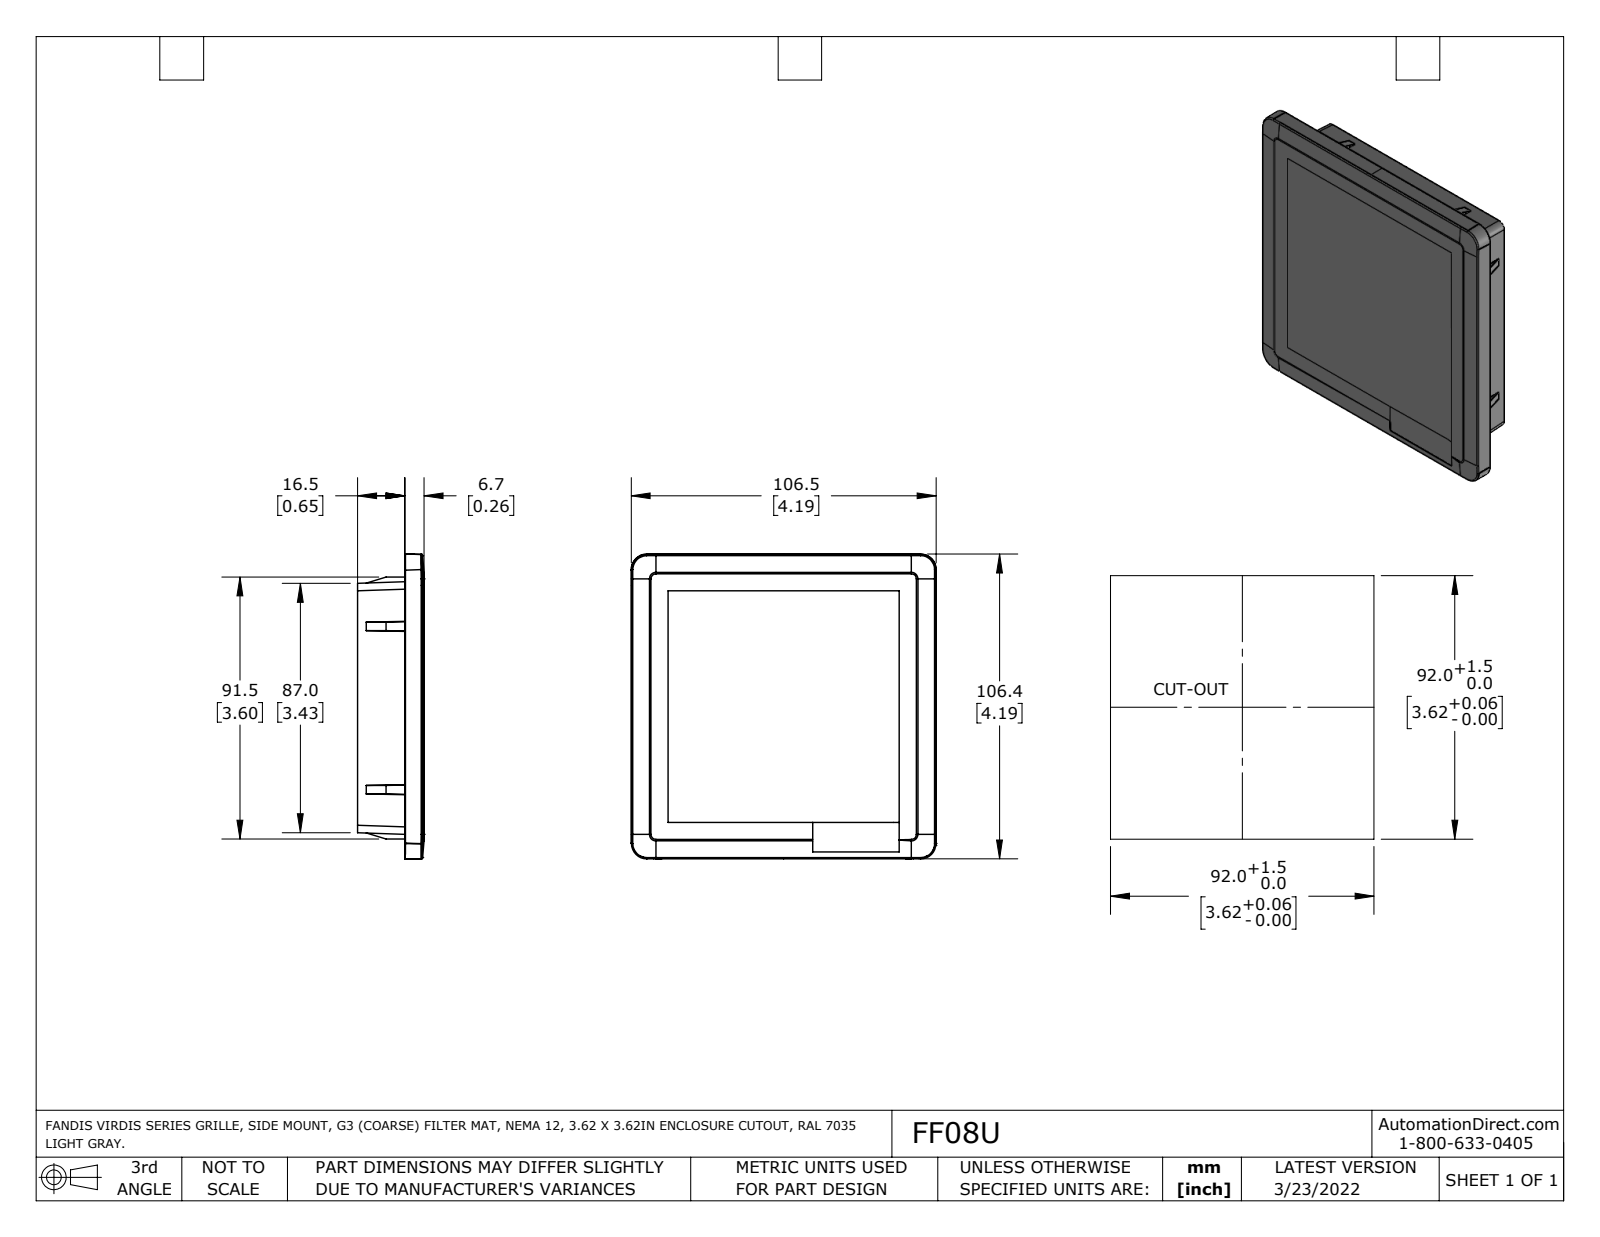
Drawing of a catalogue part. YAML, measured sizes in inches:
part_name: "FF08y (p.c.)_REV4"
step_written_by: "SolidWorks 2021 (AUTOMOTIVE_DESIGN)"
units: inches
bodies: {solids: 1, faces: 146, planar: 65, cylindrical: 21, other: 60}
overall_size: [4.193, 4.19, 0.914]
volume: 12.08
surface_area: 49
partial_cylinders:
  - {radius: 0.02, count: 7}
  - {radius: 0.059, count: 4}
  - {radius: 0.102, count: 4}
  - {radius: 0.238, count: 4}
face_to_face_distances: [0.894, 0.02, 0.914, 0.206, 0.185, 0.709, 0.265, 0.244, 0.059, 0.65]
